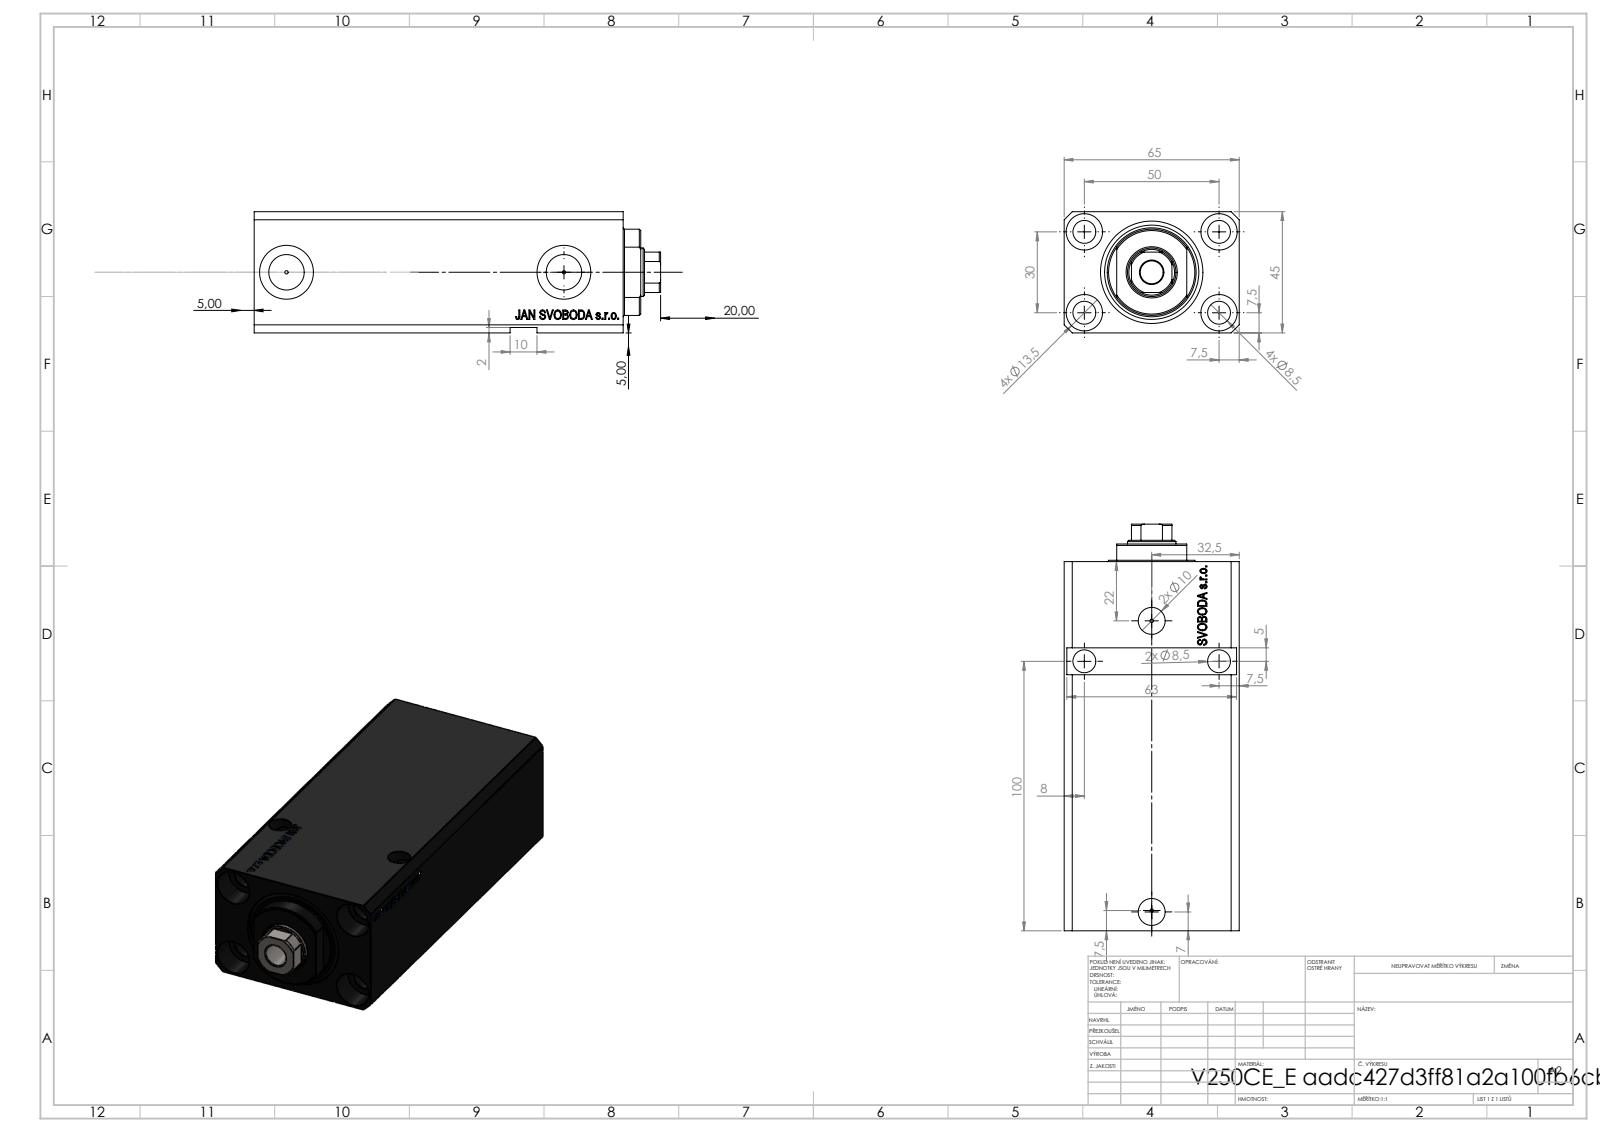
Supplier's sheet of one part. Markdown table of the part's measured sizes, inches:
| quantity | value |
| --- | --- |
| part name | V250CE_C_VCP; V250CE_E_Body; V250CE_VC_E |
| STEP written by | SolidWorks 2019 (CONFIG_CONTROL_DESIGN) |
| units | inches |
| bodies | 3 solids, 917 faces (435 planar, 104 cylindrical, 378 other) |
| overall size | 5.945 × 2.559 × 1.772 |
| volume | 20.43 in³ |
| surface area | 124.9 in² |
| round holes (diameter × count) | 0.335 × 9, 0.049 × 4, 0.531 × 4, 0.394 × 2, 0.518 × 2, 0.787 × 2, 0.709 × 1, 0.984 × 1, 1.496 × 1 |
| partial cylindrical surfaces (radius × count) | 0.335 × 1, 0.63 × 1 |
| main face-to-face distances | 1.772, 2.559, 4.843, 0.551, 5.394, 0.272, 4.571, 5.122, 1.693, 0.354 |
| hole center spacings | 1.148, 1.969, 1.181, 1.323, 1.337, 2.296, 2.756, 3.387 |
